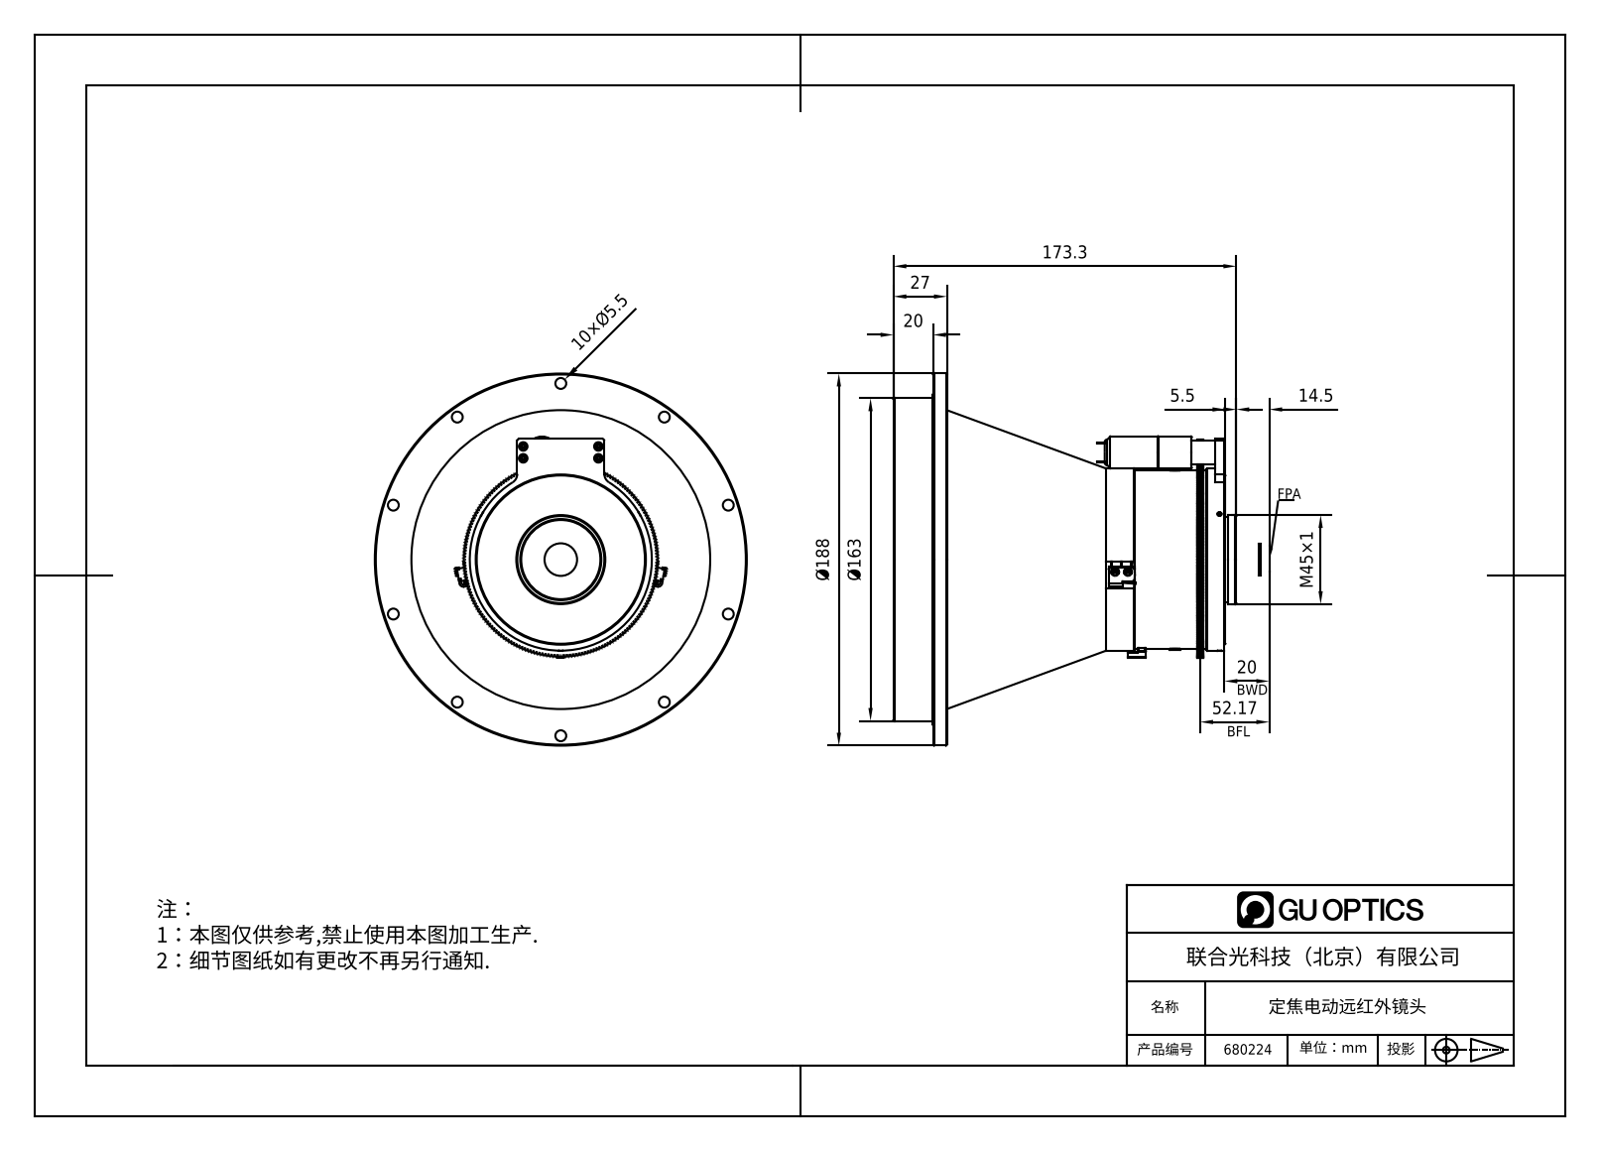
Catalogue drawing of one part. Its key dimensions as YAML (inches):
part_name: "LB-0005-2150F1电动镜头外形图-20220302"
step_written_by: "SolidWorks 2020 (CONFIG_CONTROL_DESIGN)"
units: inches
bodies: {solids: 0, faces: 2162, planar: 442, cylindrical: 1149, other: 571}
overall_size: [7.402, 7.402, 7.393]
round_holes:
  - {diameter: 0.217, count: 10}
  - {diameter: 0.063, count: 8}
  - {diameter: 0.094, count: 8}
  - {diameter: 0.081, count: 7}
  - {diameter: 0.087, count: 4}
  - {diameter: 0.169, count: 4}
  - {diameter: 0.02, count: 2}
  - {diameter: 0.031, count: 2}
  - {diameter: 0.315, count: 1}
  - {diameter: 1.575, count: 1}
  - {diameter: 6.142, count: 1}
  - {diameter: 6.201, count: 1}
round_bosses_or_shafts:
  - {diameter: 0.079, count: 12}
  - {diameter: 0.15, count: 4}
  - {diameter: 0.138, count: 4}
  - {diameter: 0.394, count: 2}
  - {diameter: 0.236, count: 2}
  - {diameter: 0.118, count: 2}
  - {diameter: 7.402, count: 1}
  - {diameter: 6.417, count: 1}
partial_cylinders:
  - {radius: 0.007, count: 488}
  - {radius: 0.012, count: 16}
  - {radius: 0.039, count: 16}
  - {radius: 0.02, count: 8}
  - {radius: 0.008, count: 2}
  - {radius: 0.01, count: 2}
  - {radius: 0.016, count: 2}
  - {radius: 0.079, count: 2}
face_to_face_distances: [0.276, 5.542, 5.818, 0.02, 5.522, 5.798, 0.118, 0.562, 0.542, 4.98]
hole_center_spacings: [2.165, 3.504, 4.119, 5.669, 6.665, 0.256, 7.007, 0.197]
